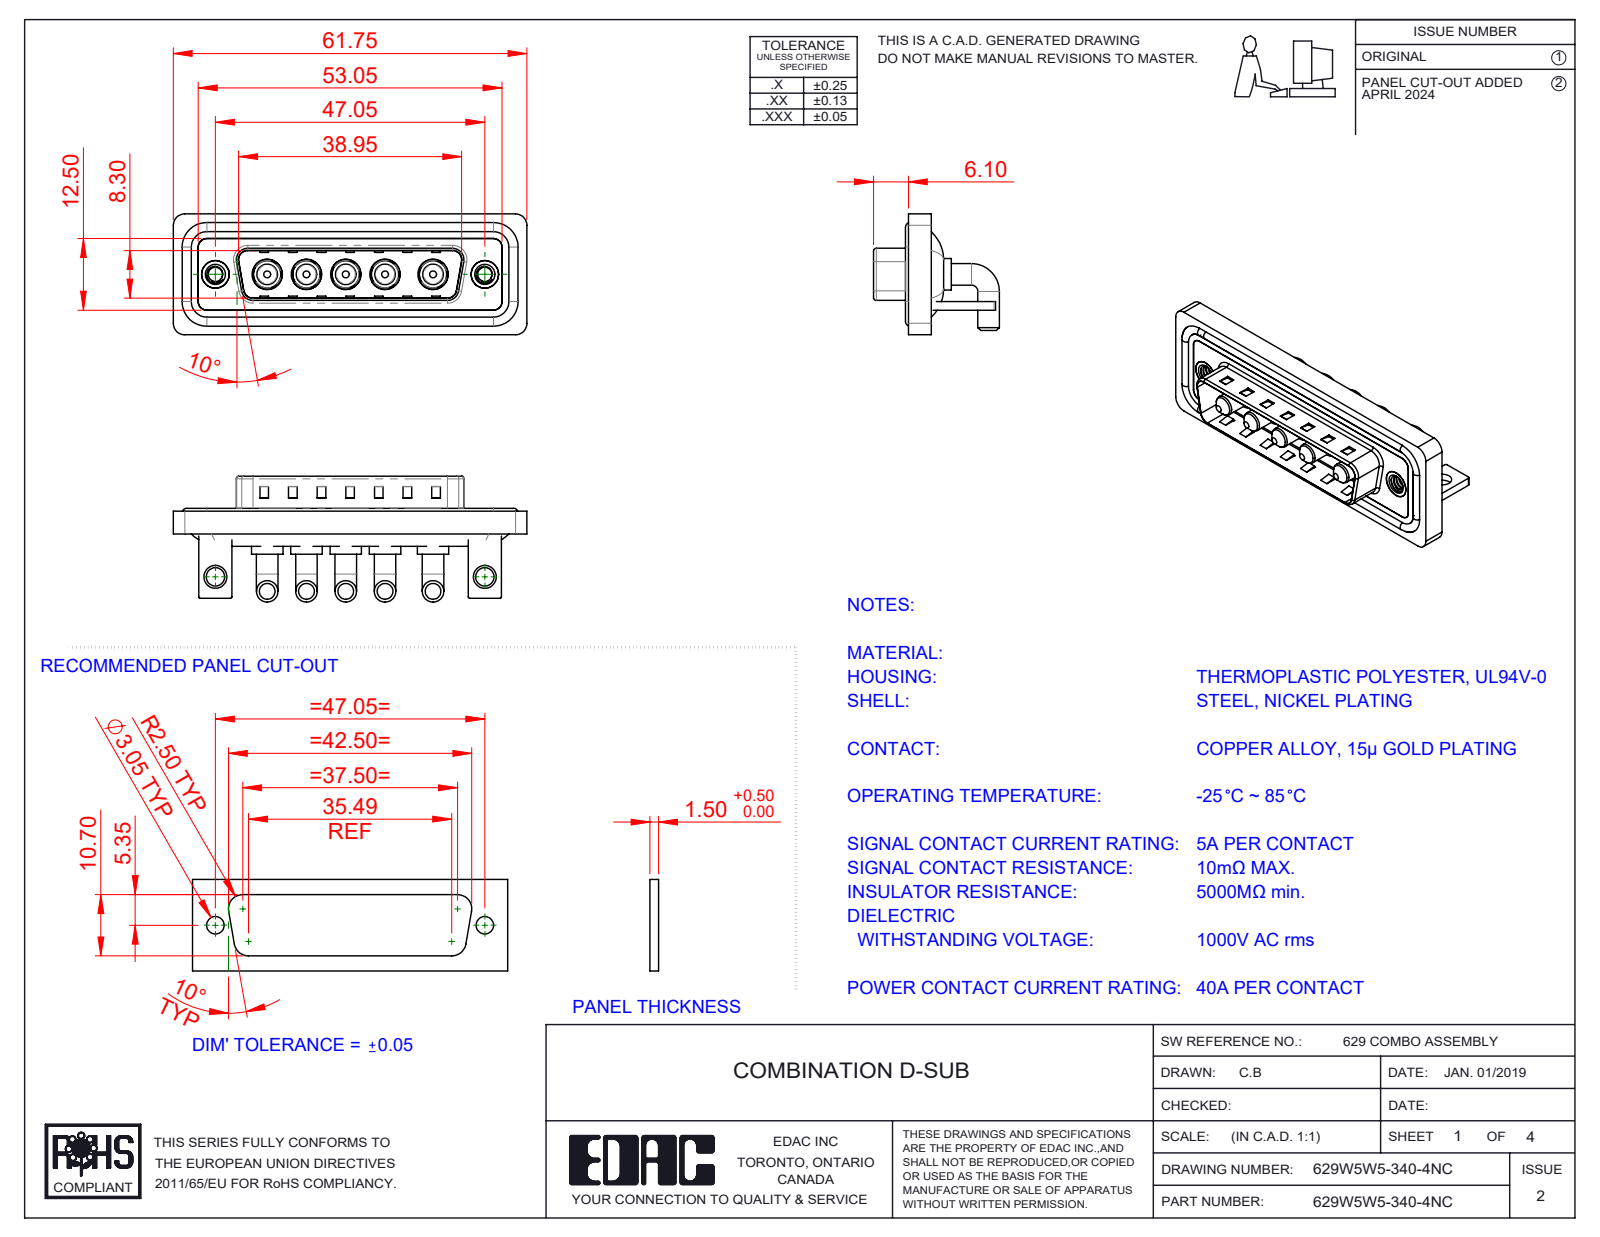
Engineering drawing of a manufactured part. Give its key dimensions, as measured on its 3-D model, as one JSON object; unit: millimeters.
{"part_name": "629Combo Shell Rear_25 Contacts; 629W5W5-340-4NC; Power Pin_40A RA; 629Combo Waterproof Housing_25 Contacts (+4 more)", "step_written_by": "SolidWorks 2023 (CONFIG_CONTROL_DESIGN)", "units": "millimeters", "bodies": {"solids": 19, "faces": 736, "planar": 279, "cylindrical": 311, "other": 146}, "overall_size": [61.75, 21.98, 21.1], "volume_mm3": 8439, "surface_area_mm2": 13079, "round_holes": [[4.85, 5], [5.3, 5], [2.5, 2], [3.2, 2], [4, 2], [4.8, 2], [5, 2]], "round_bosses_or_shafts": [[3.75, 10], [5.5, 5], [5.2, 5], [4.75, 5], [3.6, 5], [1.6, 4], [4.9, 2]], "partial_cylinders_radius": [[2, 19], [1.5, 18], [0.25, 16], [0.5, 9], [1.6, 8], [2.1, 5], [0.6, 4], [0.65, 4]], "face_to_face_distances": [0.4, 1.5, 2.9, 0.8, 2.1, 3.7, 1.1, 4.5, 4.1, 1.2], "hole_center_spacings": [6.86, 13.73, 47.05, 6.85, 6.87, 8.37, 8.38, 9.04]}
